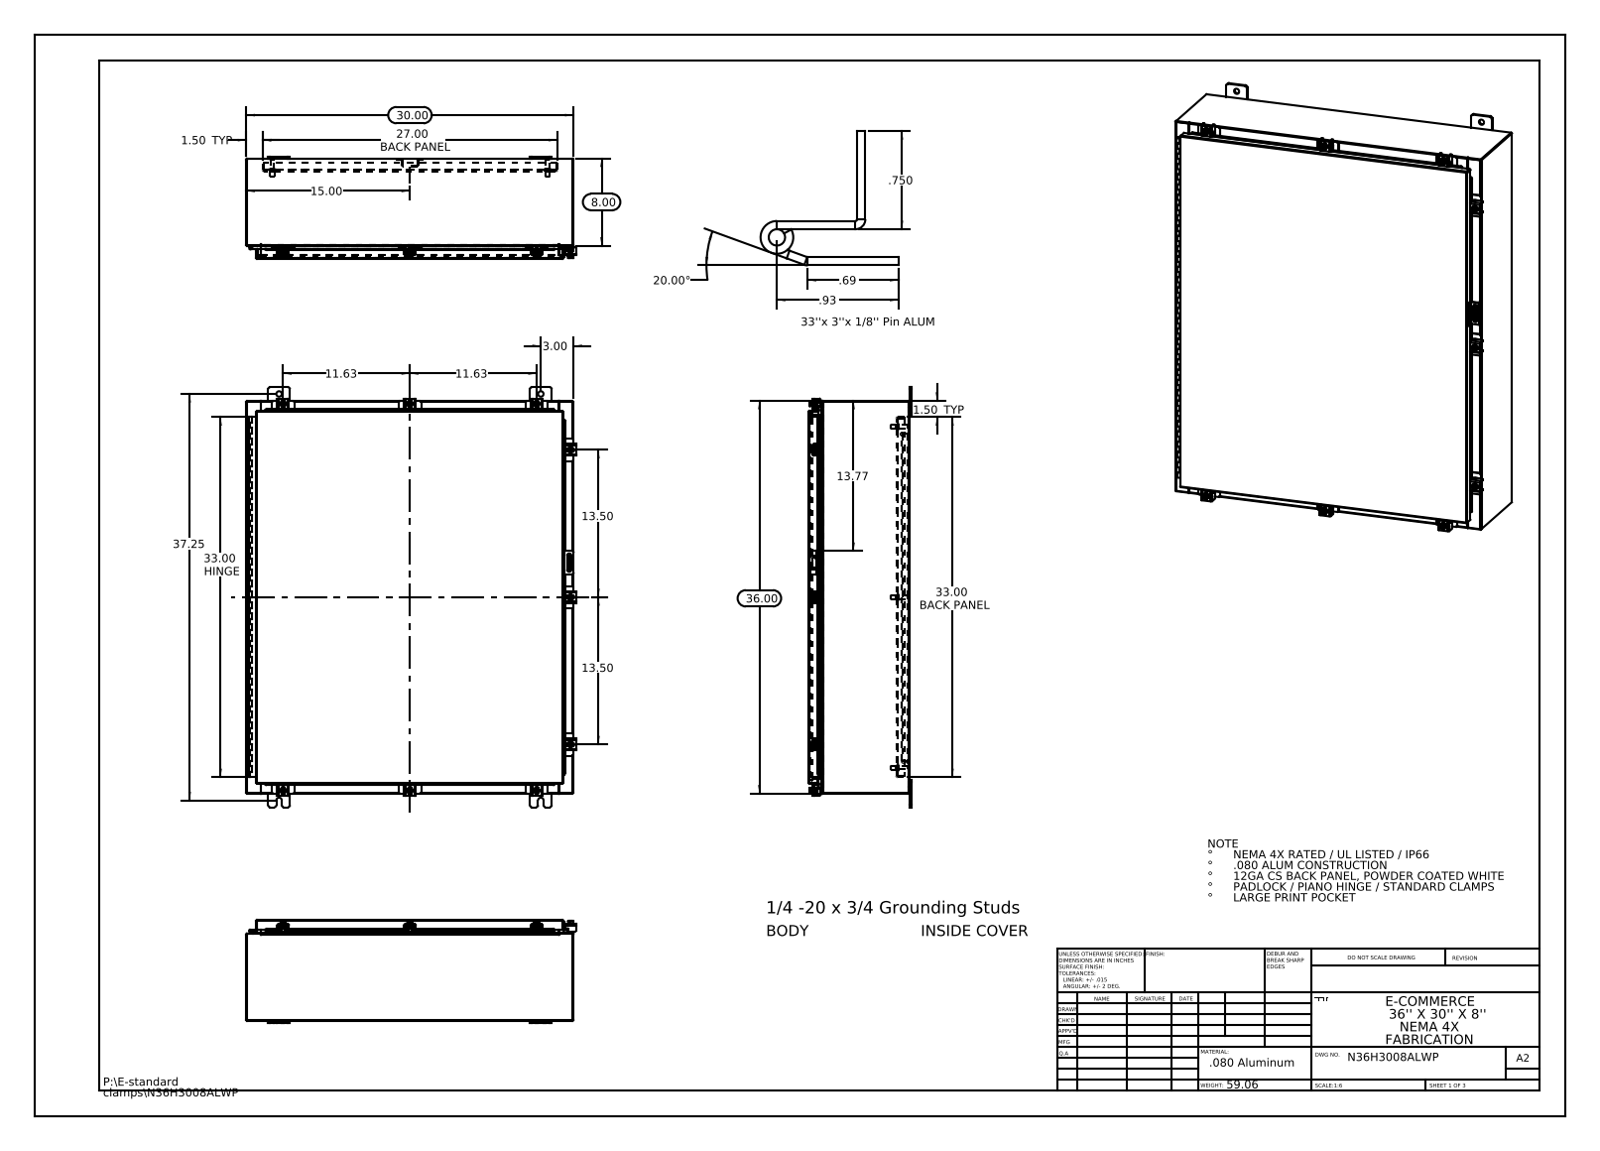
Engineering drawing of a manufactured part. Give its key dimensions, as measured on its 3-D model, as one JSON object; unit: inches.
{"part_name": "N36H3008ALWP Padlock Hasp; N36H3008ALWP Body; N36H3008ALWP Clamp Top; N36H3008ALWP Mounting Studs (+8 more)", "step_written_by": "SolidWorks 2013 (CONFIG_CONTROL_DESIGN)", "units": "inches", "bodies": {"solids": 65, "faces": 2456, "planar": 1288, "cylindrical": 1028, "other": 140}, "overall_size": [38.5, 30.211, 9.389], "volume_in3": 382.5, "surface_area_in2": 9518, "round_holes": [[0.5, 10], [0.213, 9], [0.26, 9], [0.125, 2], [0.125, 1]], "round_bosses_or_shafts": [[0.25, 10], [0.5, 9], [0.399, 9], [0.625, 6], [0.375, 6], [0.33, 6]], "partial_cylinders_radius": [[0.06, 42], [0.013, 31], [0.088, 25], [0.19, 24], [0.12, 18], [0.141, 18], [0.05, 13], [0.08, 12]], "face_to_face_distances": [0.075, 9.126, 9.051, 9.201, 0.104, 1, 8.126, 1.075, 8.051, 1.179], "hole_center_spacings": [15.625, 17.754, 29.694, 33.366, 37.309, 25.25, 35.451, 1.858]}
